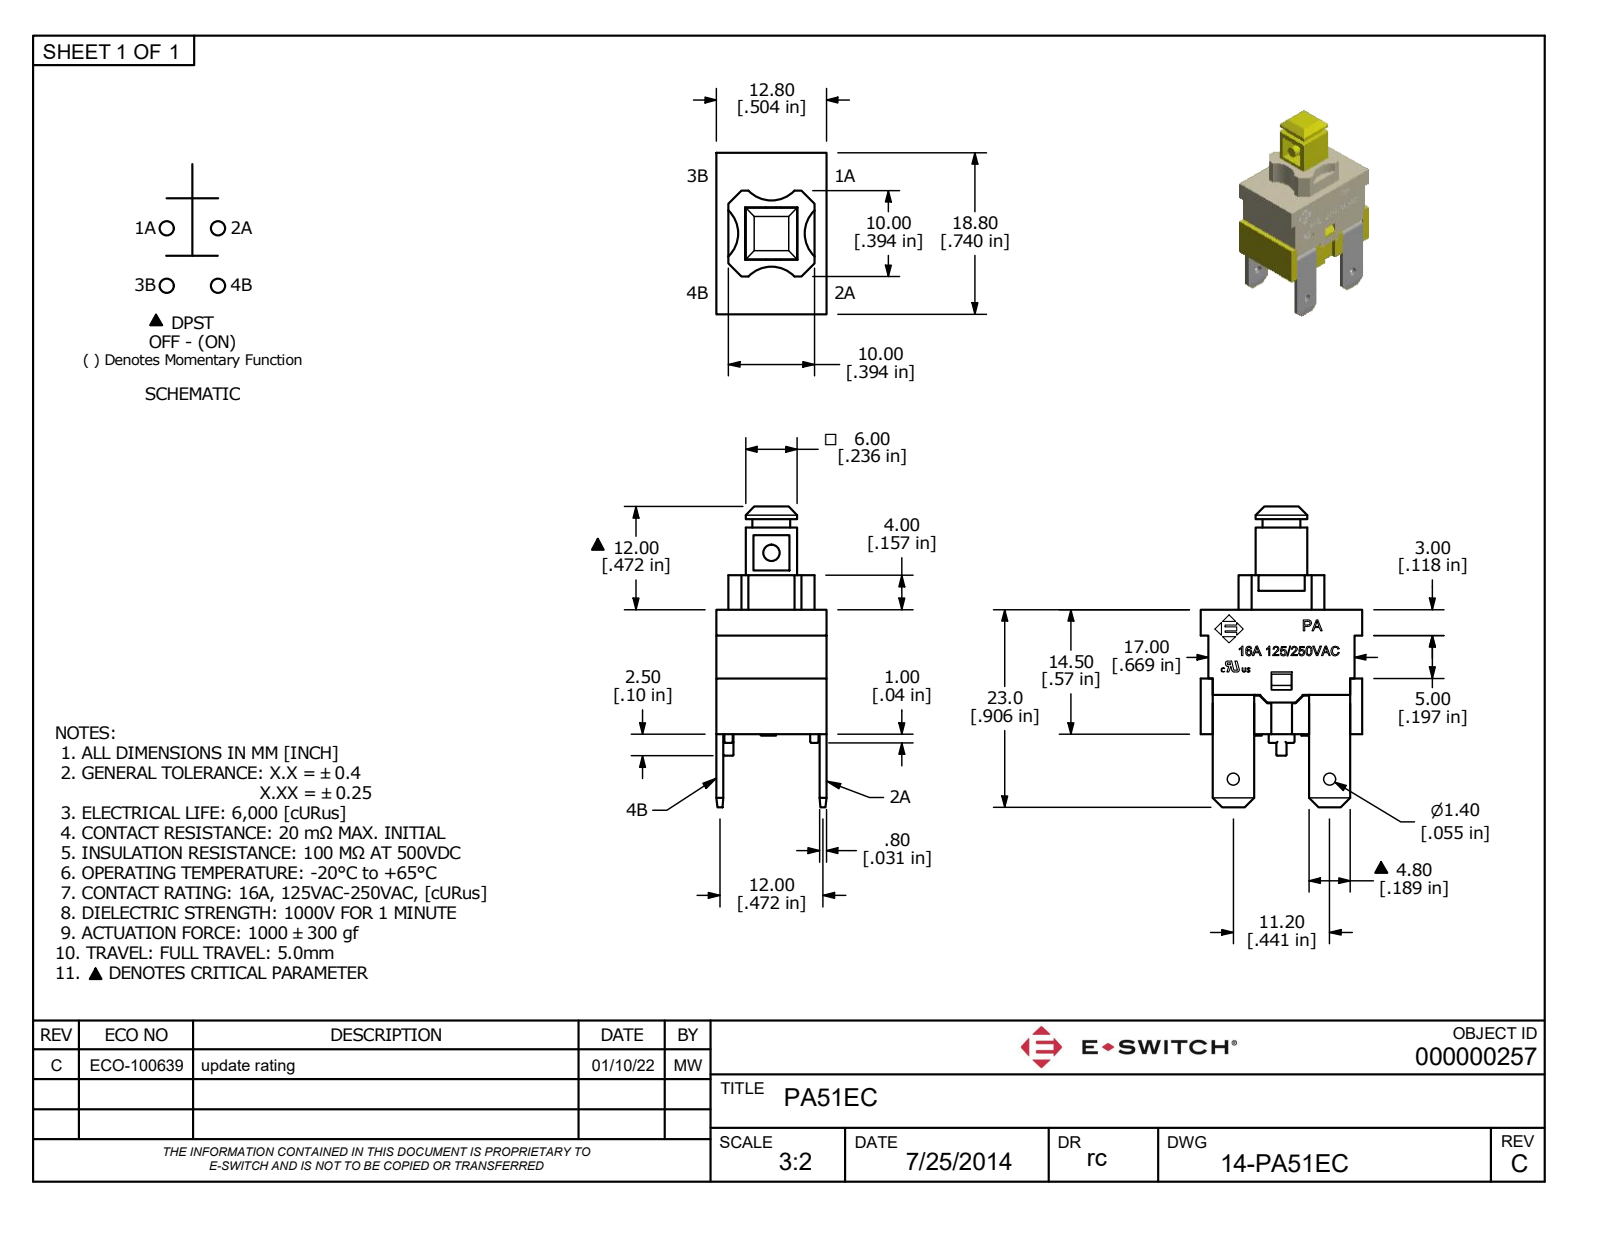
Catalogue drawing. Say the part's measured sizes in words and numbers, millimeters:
The part is named "PA51EC". Its 3-D file was written by "Autodesk Inventor 2022 (AUTOMOTIVE_DESIGN)". It is 1 solid with 843 faces: 622 planar, 90 cylindrical and 131 other. Overall it measures 35 by 18.8 by 12.8 millimeters. Its volume is 2 286 cubic millimeters and its surface area 4 612 square millimeters. Round holes: 2 of diameter 1.4, 1 of diameter 3. Round bosses or shafts: 4 of diameter 0.95, 2 of diameter 2.5, 1 of diameter 1.9. Partial cylindrical surfaces (rounded edges, fillets, slot ends): 28 of radius 0.25, 16 of radius 0.12, 8 of radius 0.15, 4 of radius 1, 4 of radius 3.71, 1 of radius 0.5, 1 of radius 1.79, 1 of radius 2.32. The main face-to-face distances are 0.8, 12, 12.8, 0.9, 16.8, 2, 11.2, 11.05, 8.6, 4.4. The hole center spacings are 11.2.
